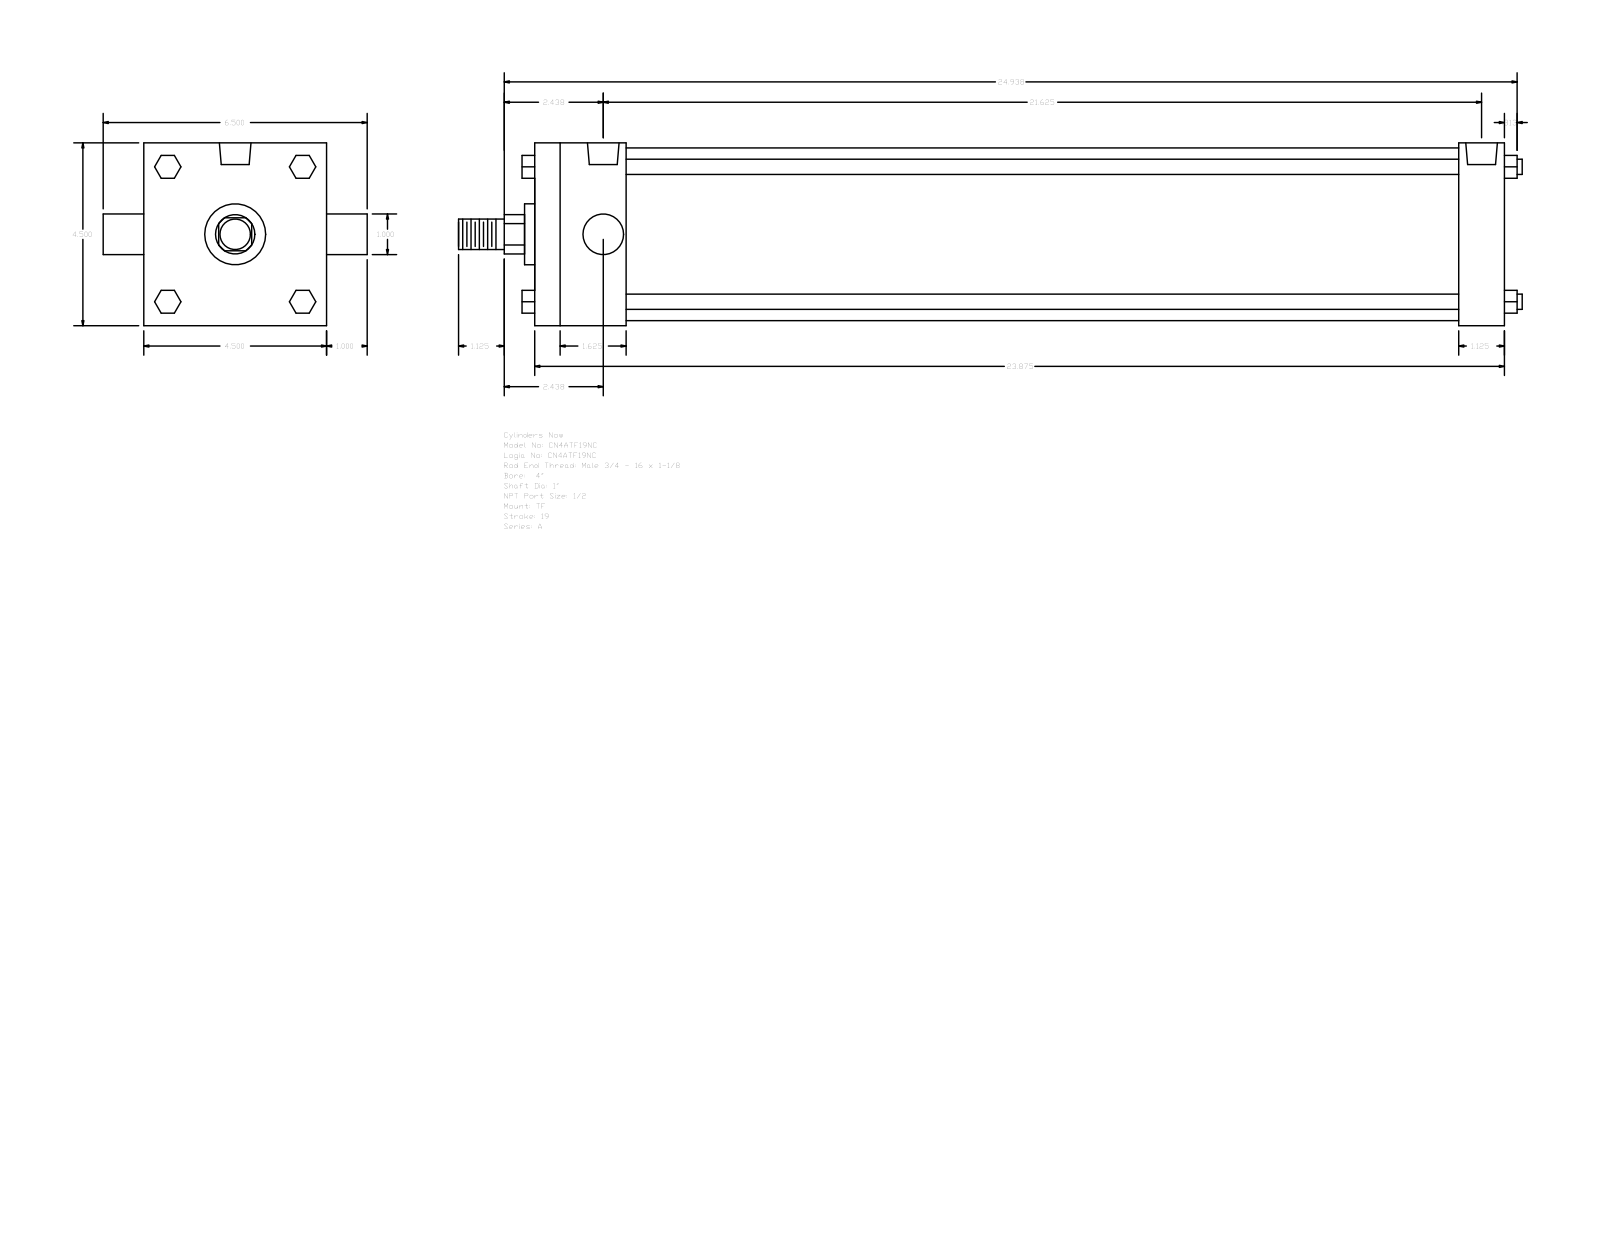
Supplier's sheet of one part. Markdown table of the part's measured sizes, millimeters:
| quantity | value |
| --- | --- |
| part name | A_TF__0400_1 |
| STEP written by | GSSL Pune (CONFIG_CONTROL_DESIGN) |
| units | millimeters |
| bodies | 0 solids, 120 faces (92 planar, 28 cylindrical, 0 other) |
| overall size | 665.16 × 165.1 × 114.3 |
| round holes (diameter × count) | 8.73 × 3, 19.77 × 2 |
| round bosses / shafts (diameter × count) | 9.53 × 4, 25.4 × 2, 107.95 × 1, 38.1 × 1, 19.05 × 1 |
| partial cylindrical surfaces (radius × count) | 12.29 × 1 |
| main face-to-face distances | 114.3, 606.43, 577.85, 28.58, 57.15, 520.7, 549.28, 14.29, 42.16, 73.03 |
| hole center spacings | 3.18, 546.1, 542.92, 549.28 |
